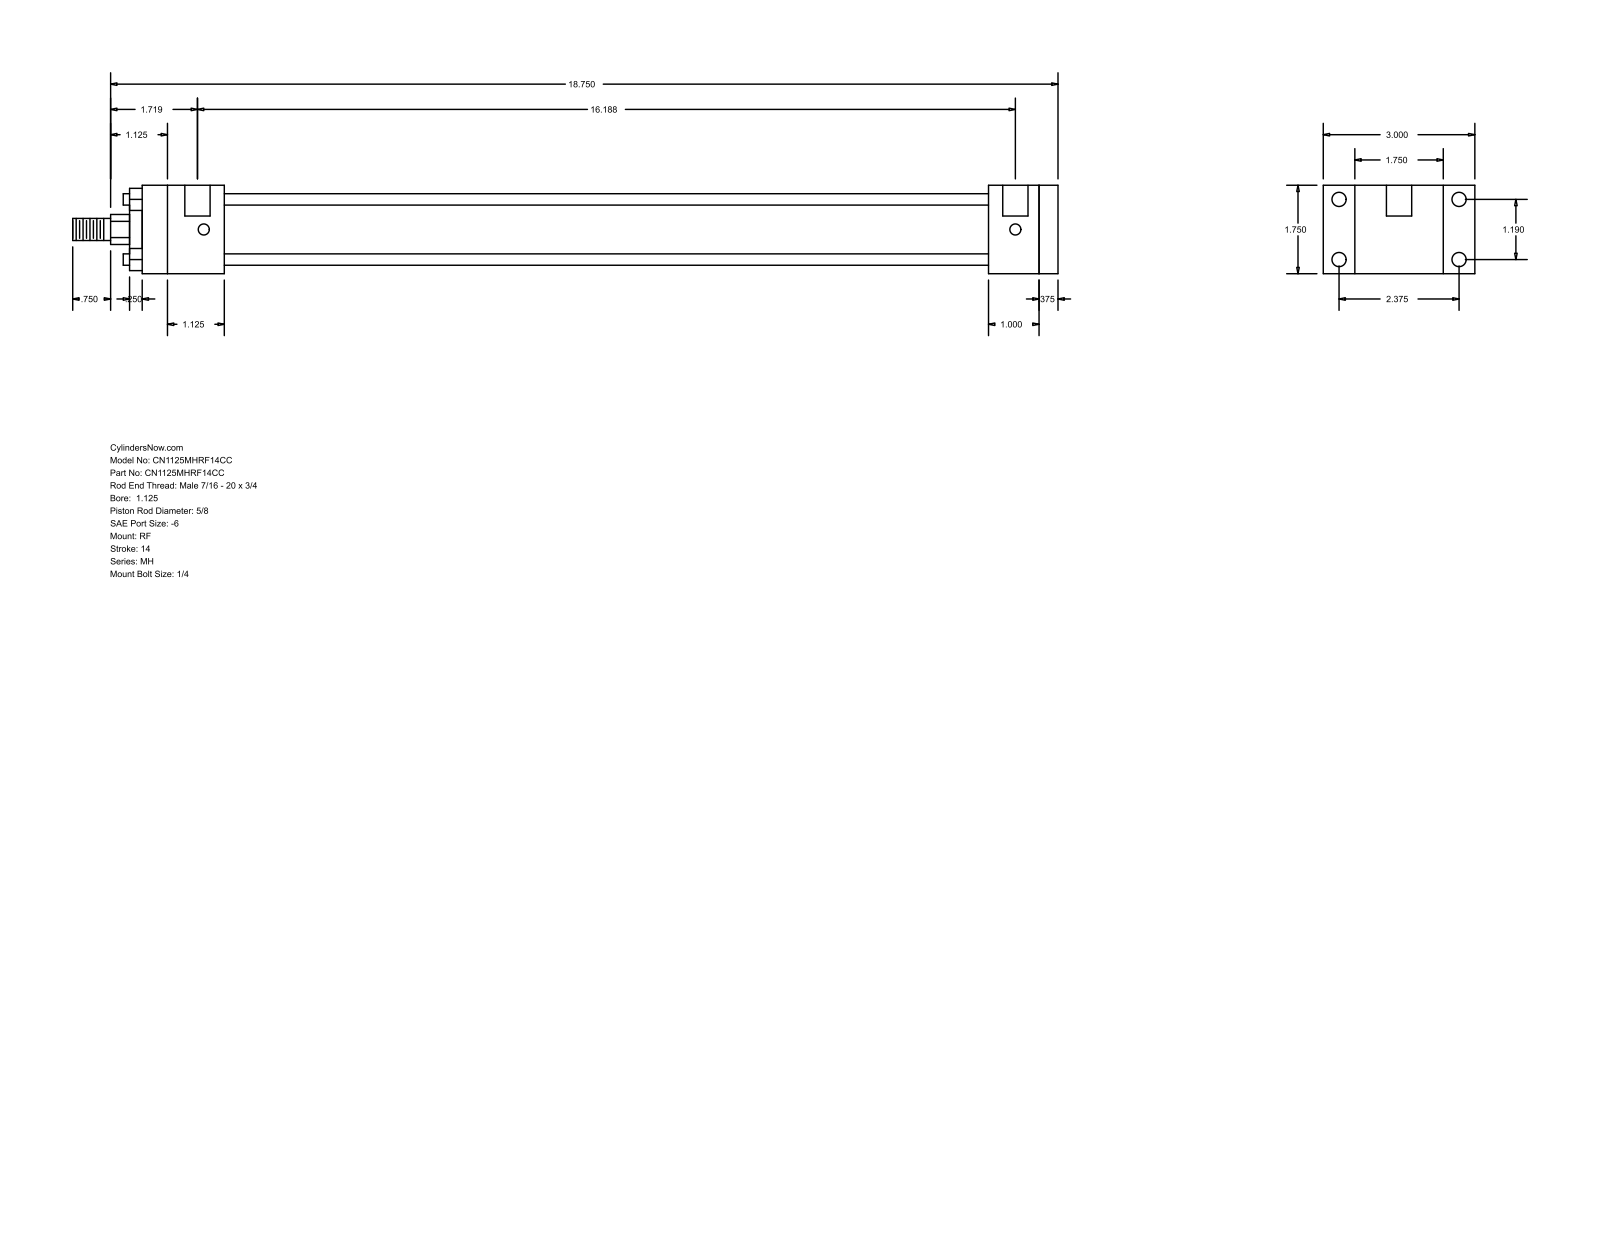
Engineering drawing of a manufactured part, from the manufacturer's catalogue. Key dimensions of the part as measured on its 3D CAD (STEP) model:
Part name (STEP PRODUCT): MH_RF__0112_0.625
STEP written by: GSSL Pune (CONFIG_CONTROL_DESIGN)
Units: millimetres
Bodies: 0 solids, 92 faces (64 planar, 28 cylindrical, 0 other)
Overall size (bounding box): 495.3 × 76.2 × 44.45
Round holes (diameter × count): ⌀5.56 ×4, ⌀7.14 ×4, ⌀12.7 ×2
Round bosses / shafts (diameter × count): ⌀5.71 ×4, ⌀34.92 ×1, ⌀28.57 ×1, ⌀15.88 ×1, ⌀11.11 ×1
Partial cylindrical surfaces — rounded edges, fillets, slot ends (radius × count): R7.54 ×1
Main face-to-face distances: 44.46, 9.52, 34.93, 460.37, 15.87, 409.58, 419.1, 384.17, 25.41, 41.27
Hole centre spacings: 30.22, 60.32, 67.47, 407.99, 3.17, 411.16
